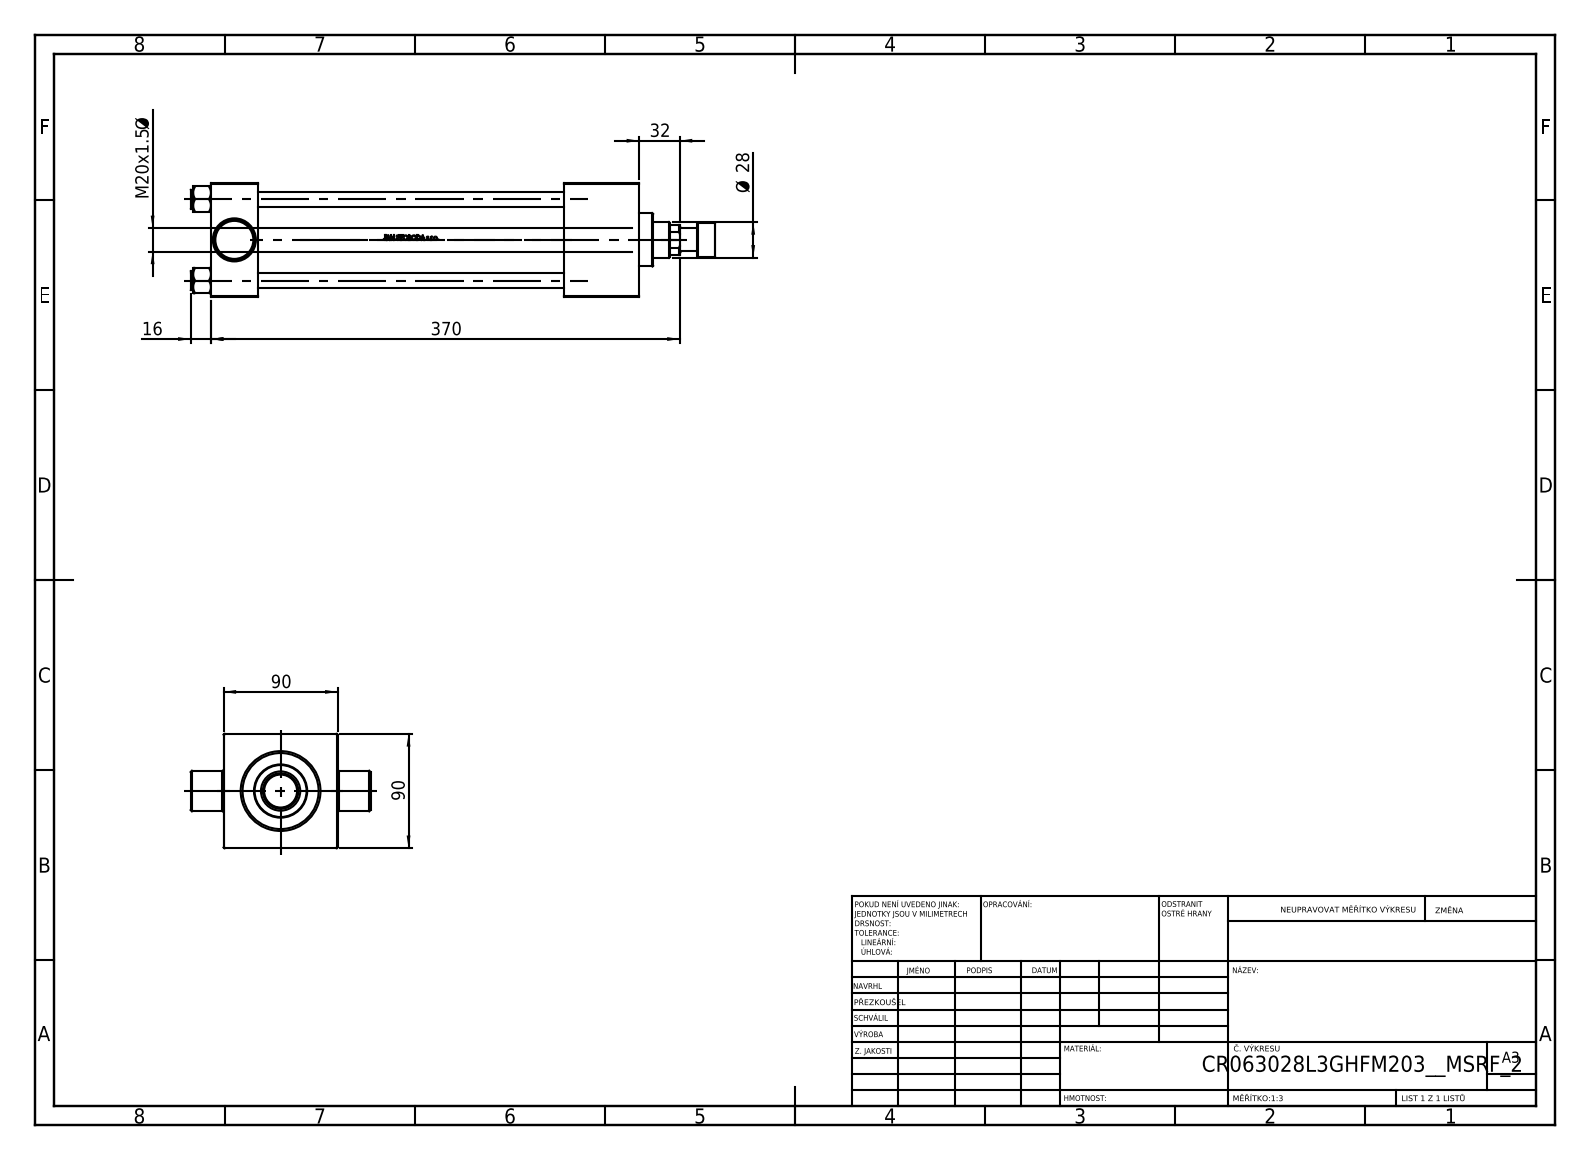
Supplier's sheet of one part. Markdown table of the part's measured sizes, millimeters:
| quantity | value |
| --- | --- |
| part name | V215CR_ROD_END_F; V215CR_VCP_L; V215CR_L_TYCINKA; V215_VC_A (+2 more) |
| STEP written by | SolidWorks 2019 (CONFIG_CONTROL_DESIGN) |
| units | millimeters |
| bodies | 12 solids, 1071 faces (429 planar, 114 cylindrical, 528 other) |
| overall size | 414 × 142 × 90 |
| volume | 1 324 000 mm³ |
| surface area | 299 557 mm² |
| round holes (diameter × count) | 12 × 4, 7 × 1, 18.5 × 1, 28 × 1, 31 × 1, 50 × 1, 60 × 1, 63 × 1 |
| round bosses / shafts (diameter × count) | 15 × 4, 69 × 1, 42 × 1, 32 × 1, 27 × 1, 18 × 1 |
| main face-to-face distances | 90, 37, 338, 301, 89, 59, 0.5, 242, 279, 89.5 |
| hole center spacings | 45.47, 64.3, 90.93 |
